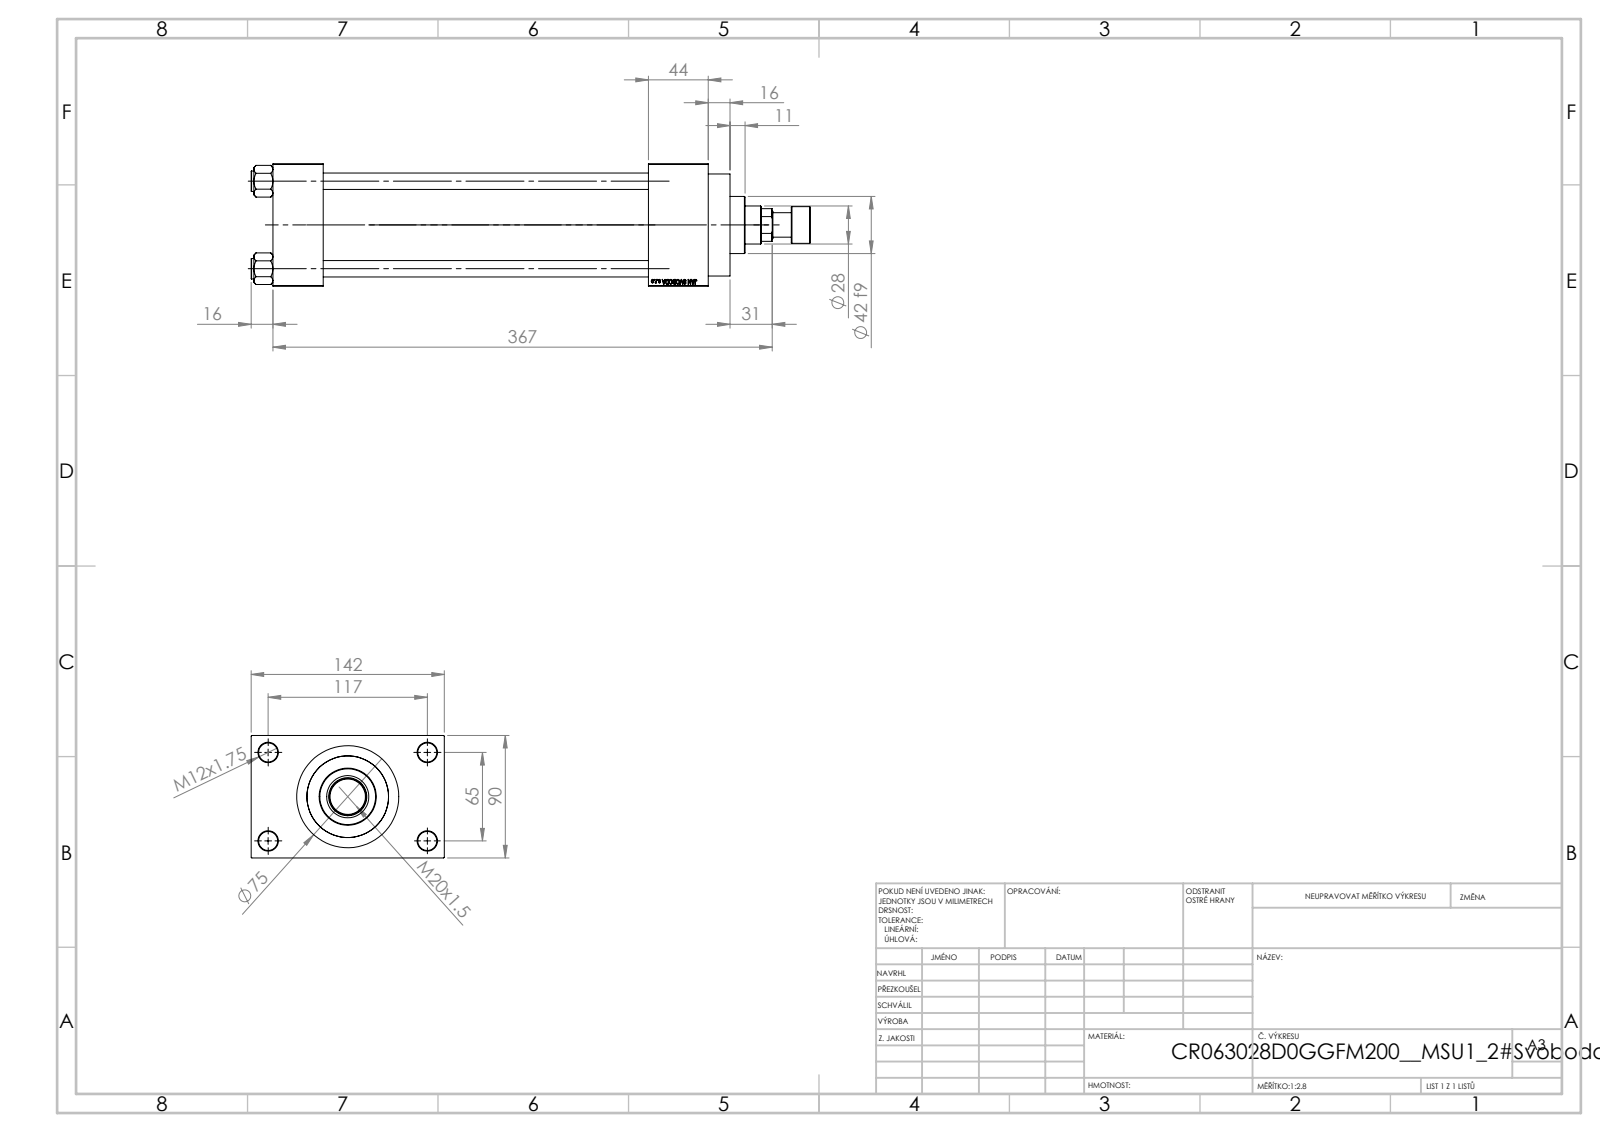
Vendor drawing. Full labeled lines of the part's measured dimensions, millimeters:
Part name (STEP PRODUCT): V215CR_D_TYCINKA; V215CR_VCP_D; V215CR_D_Body; NUT_M5_D (+2 more)
STEP written by: SolidWorks 2019 (CONFIG_CONTROL_DESIGN)
Units: millimetres
Bodies: 12 solids, 1118 faces (501 planar, 93 cylindrical, 524 other)
Overall size (bounding box): 411 × 142 × 90
Volume: 1 421 000 mm³ · Surface area: 319 485 mm²
Round holes (diameter × count): ⌀12 ×4, ⌀14 ×4, ⌀7 ×2, ⌀20.96 ×2, ⌀30 ×2, ⌀18.5 ×1, ⌀28 ×1, ⌀31 ×1, ⌀50 ×1, ⌀60 ×1, ⌀63 ×1
Round bosses / shafts (diameter × count): ⌀15 ×4, ⌀75 ×1, ⌀69 ×1, ⌀42 ×1, ⌀27 ×1, ⌀18 ×1
Main face-to-face distances: 90, 239, 37, 276, 283, 320, 44, 26, 116, 142
Hole centre spacings: 26.35, 45.47, 64.3, 66.92, 69.81, 90.65, 111.34, 65
